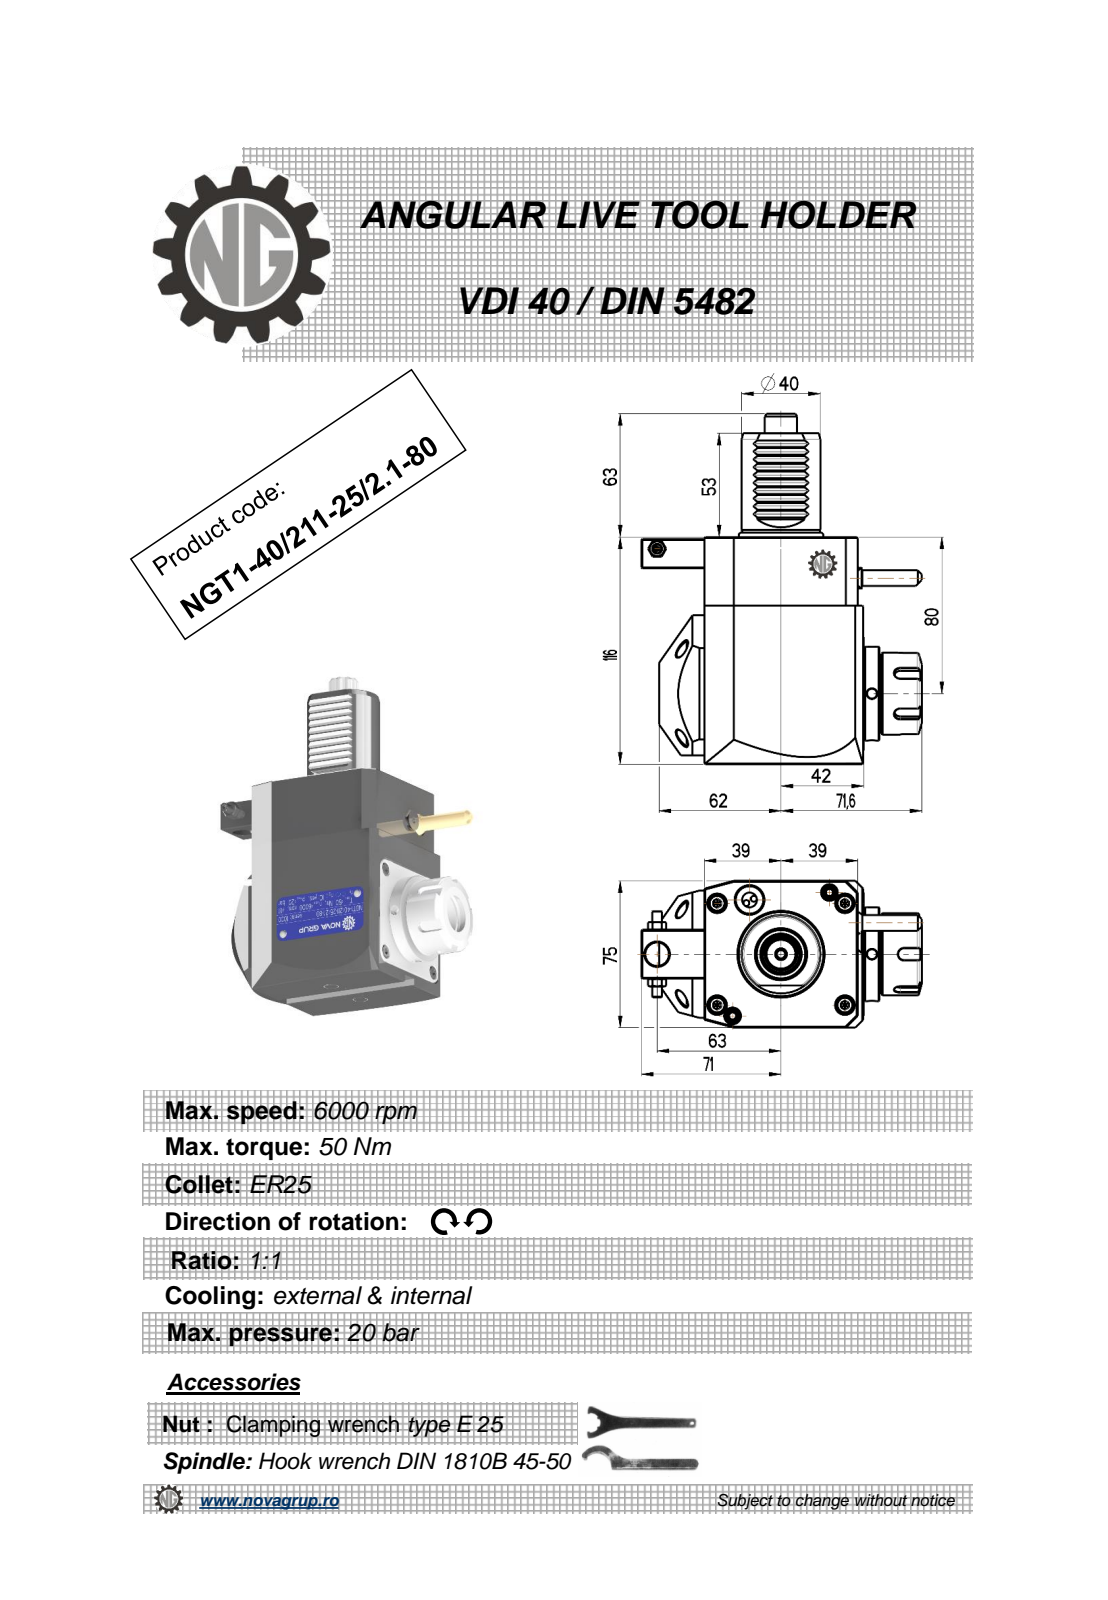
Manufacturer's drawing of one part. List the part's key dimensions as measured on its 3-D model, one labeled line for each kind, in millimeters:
Part name (STEP PRODUCT): NGT1_40_211_25_2_1_80
STEP written by: PRO/ENGINEER BY PARAMETRIC TECHNOLOGY CORPORATION, 2010280 (CONFIG_CONTROL_DESIGN)
Units: millimetres
Bodies: 1 solid, 480 faces (190 planar, 124 cylindrical, 166 other)
Overall size (bounding box): 179 × 142.6 × 76.6
Volume: 864 487 mm³ · Surface area: 69 567 mm²
Round holes (diameter × count): ⌀5 ×3, ⌀4.2 ×2, ⌀3 ×1, ⌀9.5 ×1, ⌀12 ×1, ⌀20.3 ×1
Round bosses / shafts (diameter × count): ⌀48 ×1, ⌀42 ×1, ⌀40 ×1, ⌀37.5 ×1, ⌀33 ×1, ⌀11.2 ×1, ⌀8.96 ×1, ⌀8 ×1
Partial cylindrical surfaces — rounded edges, fillets, slot ends (radius × count): R3.03 ×18, R0.26 ×12, R0.3 ×10, R0.22 ×6, R3 ×5, R0.5 ×1, R6.75 ×1, R8.22 ×1
Main face-to-face distances: 75, 116, 81, 3, 78, 80.8, 2.8, 112, 25, 7.5
Hole centre spacings: 20.93, 46.25, 61.13, 63, 72.5, 109.25, 131.95
